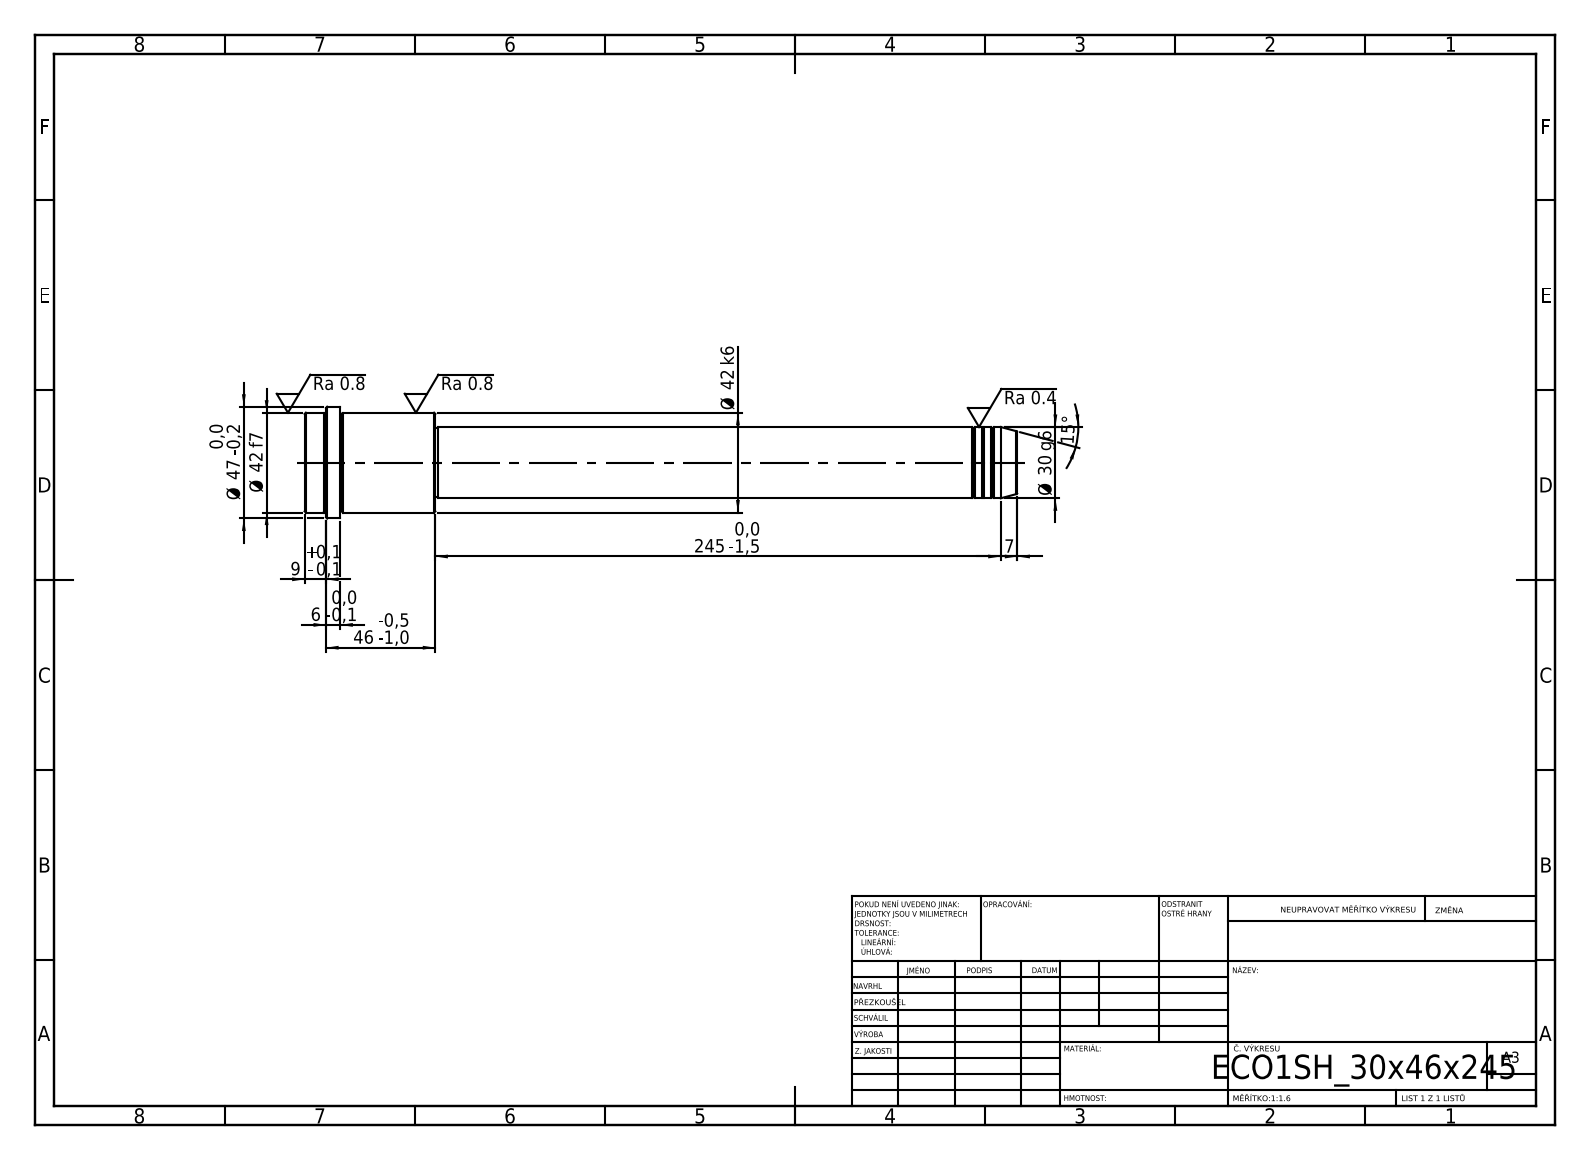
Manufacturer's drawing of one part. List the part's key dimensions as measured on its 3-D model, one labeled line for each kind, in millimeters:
STEP written by: SolidWorks 2019 (CONFIG_CONTROL_DESIGN)
Units: millimetres
Bodies: 1 solid, 52 faces (6 planar, 16 cylindrical, 30 other)
Overall size (bounding box): 300 × 47 × 47
Volume: 250 572 mm³ · Surface area: 33 982 mm²
Round bosses / shafts (diameter × count): ⌀47 ×1, ⌀42 ×1, ⌀30 ×1, ⌀29 ×1
Main face-to-face distances: 55, 245, 300, 285, 40, 15, 291, 46, 6, 9
